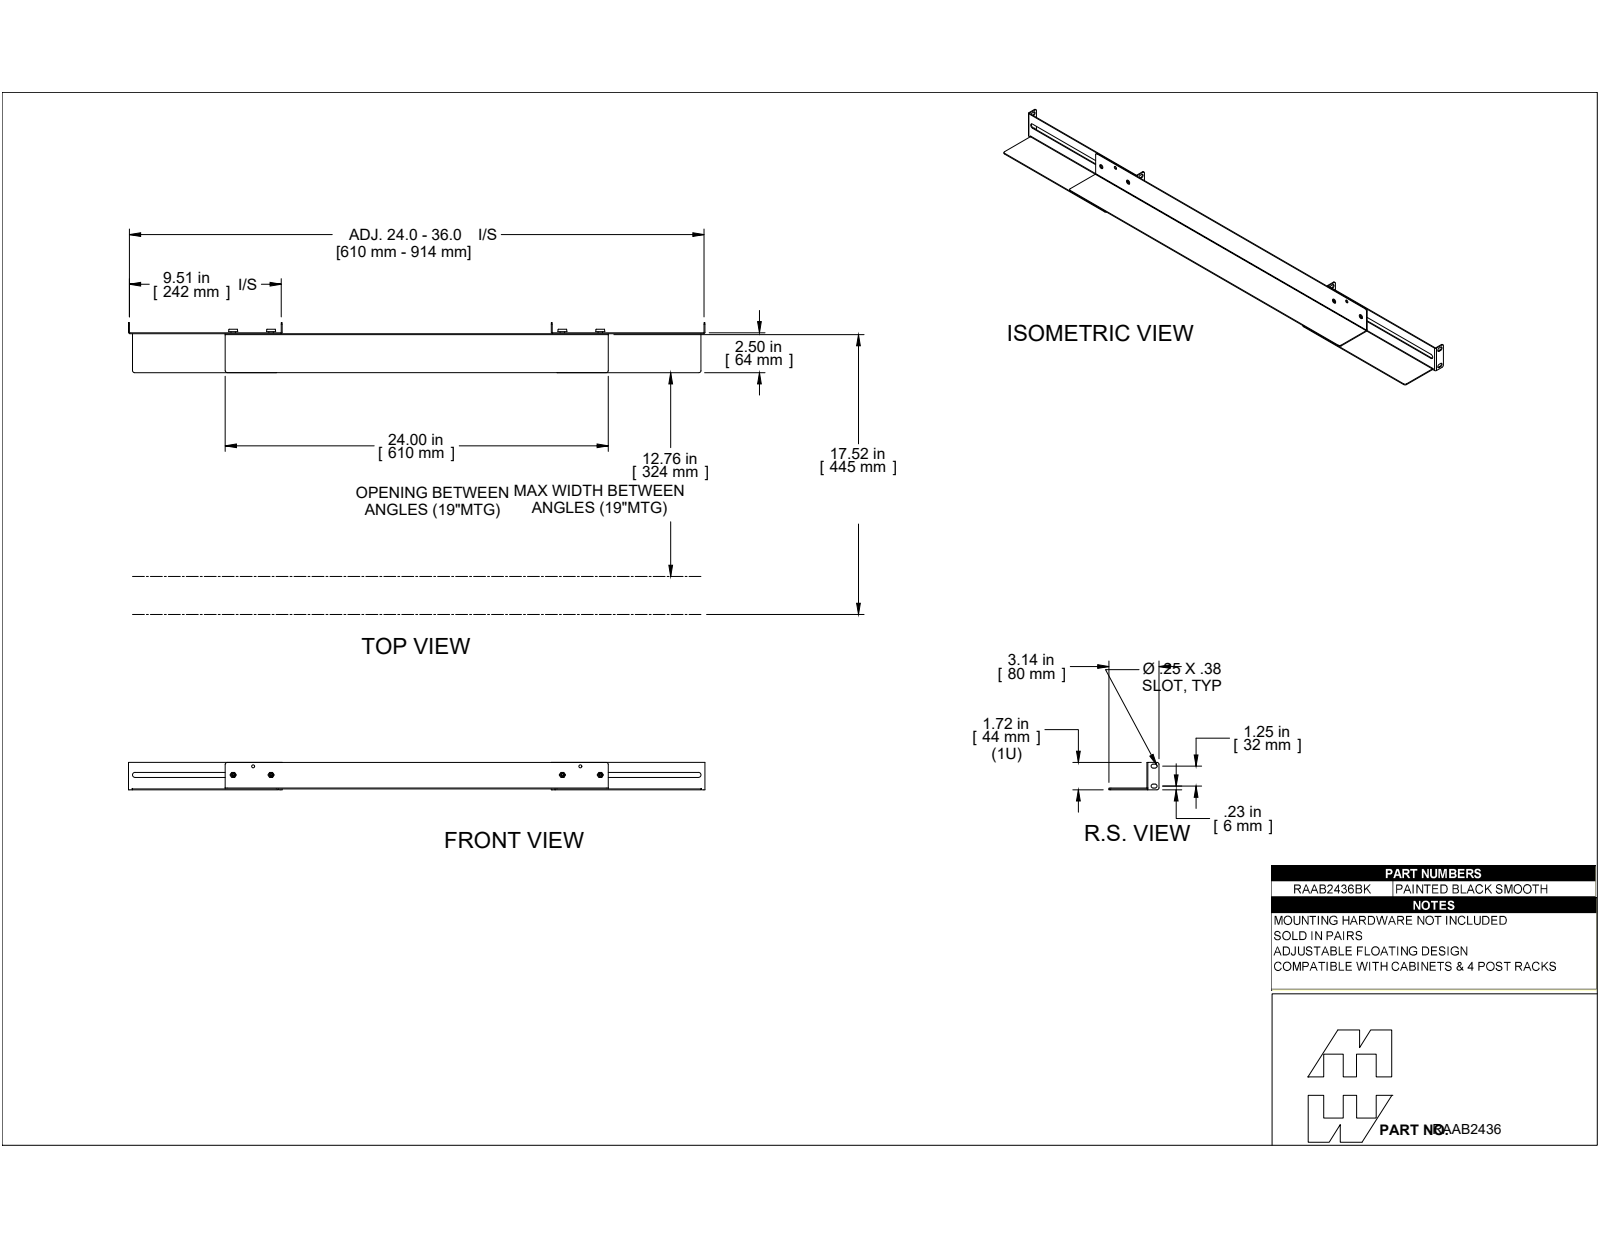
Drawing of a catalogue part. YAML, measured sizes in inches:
part_name: "RAAB2436BK"
step_written_by: "SolidWorks 2019 (AUTOMOTIVE_DESIGN)"
units: inches
bodies: {solids: 15, faces: 312, planar: 188, cylindrical: 72, other: 52}
overall_size: [36.114, 3.143, 1.718]
volume: 9.905
surface_area: 358
round_holes:
  - {diameter: 0.159, count: 4}
  - {diameter: 0.281, count: 4}
  - {diameter: 0.187, count: 2}
round_bosses_or_shafts:
  - {diameter: 0.277, count: 4}
  - {diameter: 0.19, count: 4}
  - {diameter: 0.148, count: 4}
partial_cylinders:
  - {radius: 0.125, count: 16}
  - {radius: 0.029, count: 6}
  - {radius: 0.086, count: 6}
  - {radius: 0.157, count: 4}
face_to_face_distances: [0.057, 0.114, 26.489, 9.568, 9.625, 26.546, 36.057, 9.511, 26.432, 16.921]
hole_center_spacings: [1.36, 21.757, 1.246, 1.246, 2.375, 2.375, 18.25, 19.382]
